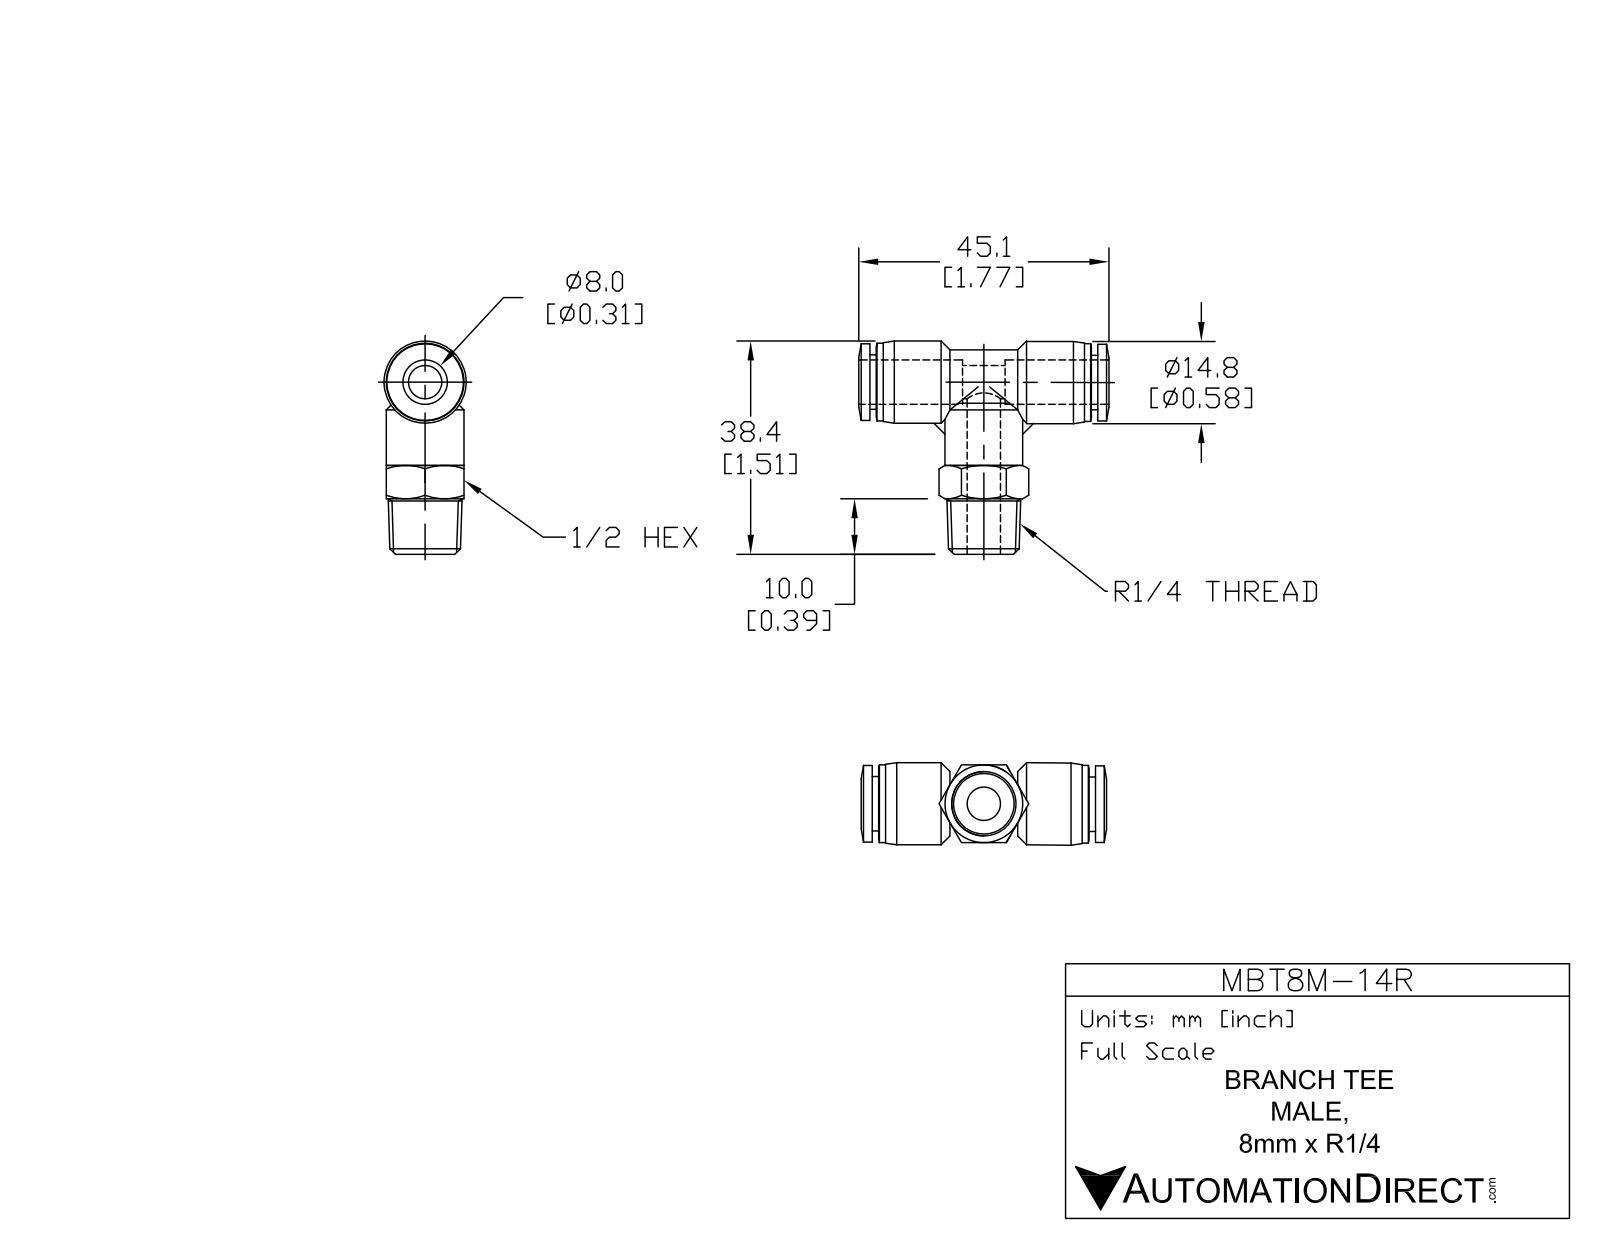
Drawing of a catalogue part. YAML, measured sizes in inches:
part_name: "MBT8M-14R"
step_written_by: "SolidWorks 2015 (AUTOMOTIVE_DESIGN)"
units: inches
bodies: {solids: 1, faces: 100, planar: 25, cylindrical: 33, other: 42}
overall_size: [1.78, 1.516, 0.591]
volume: 0.453
surface_area: 8.192
round_holes:
  - {diameter: 0.236, count: 2}
  - {diameter: 0.327, count: 1}
round_bosses_or_shafts:
  - {diameter: 0.591, count: 1}
  - {diameter: 0.559, count: 1}
  - {diameter: 0.551, count: 1}
  - {diameter: 0.543, count: 1}
  - {diameter: 0.457, count: 1}
  - {diameter: 0.386, count: 1}
partial_cylinders:
  - {radius: 0.228, count: 1}
face_to_face_distances: [0.551, 0.045, 1.577, 1.622, 0.642, 0.98, 0.596, 0.935, 1.531, 0.339]
